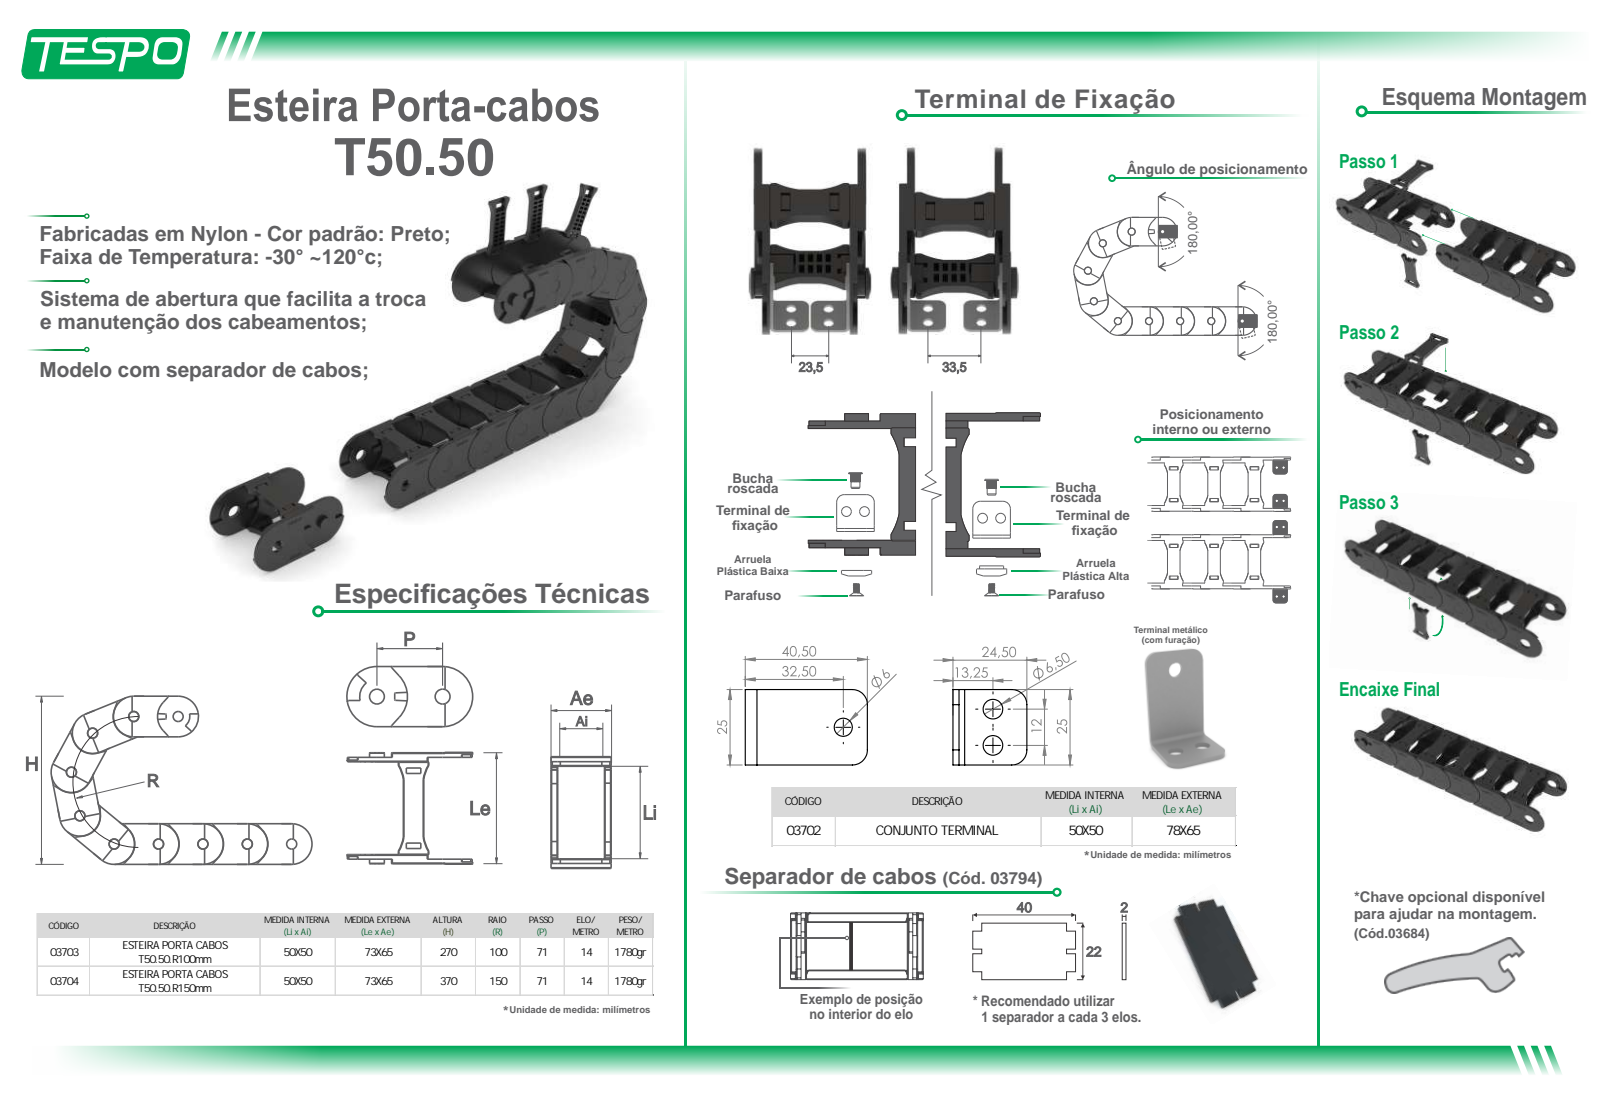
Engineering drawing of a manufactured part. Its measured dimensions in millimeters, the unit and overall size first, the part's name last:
Units: millimetres
Overall size (bounding box): 136 × 70 × 65
Volume: 108 620 mm³ · Surface area: 48 110 mm²
Bodies: 4 solids, 150 faces (0 planar, 0 cylindrical, 150 other)
STEP written by: ST-DEVELOPER v15 (AUTOMOTIVE_DESIGN)
